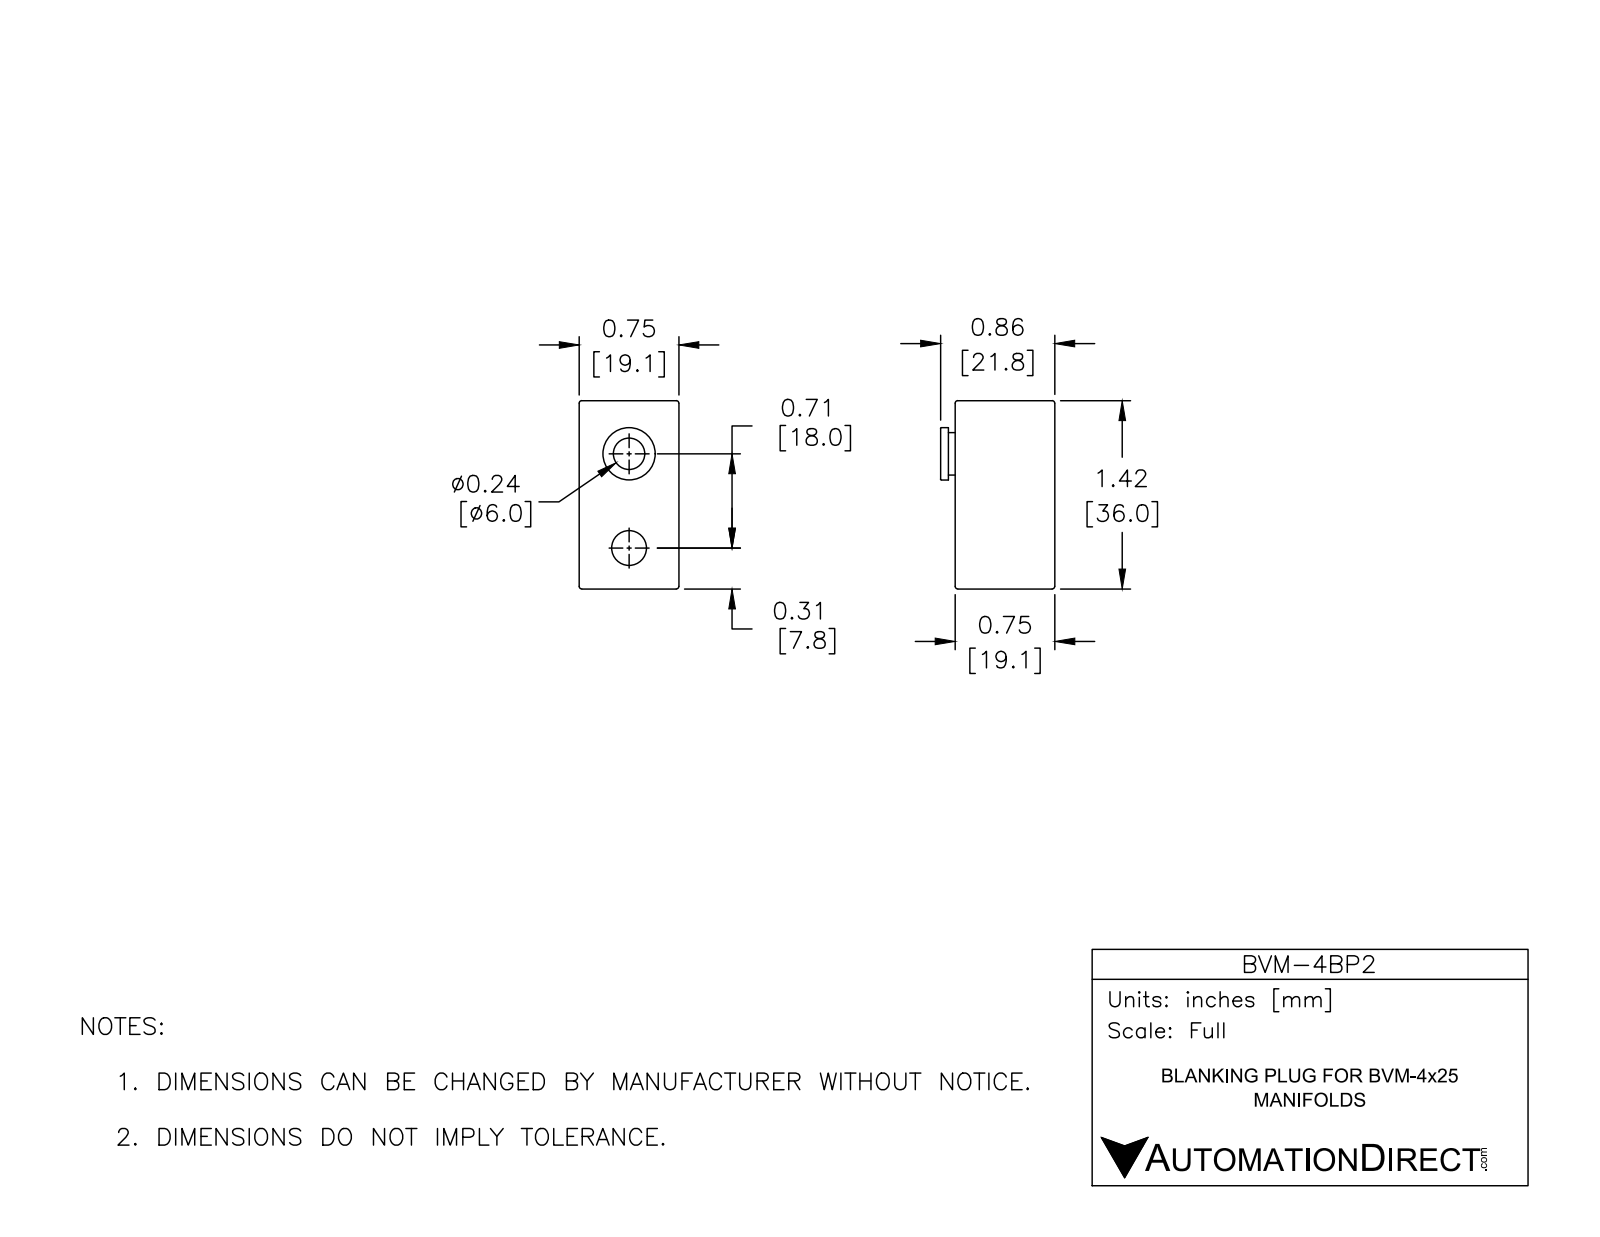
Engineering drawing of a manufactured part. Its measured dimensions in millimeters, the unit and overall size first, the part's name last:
Units: millimetres
Overall size (bounding box): 35.99 × 21.84 × 19.05
Round holes (diameter × count): ⌀6.25 ×2, ⌀6.4 ×1, ⌀7.92 ×1, ⌀10.82 ×1
Round bosses / shafts (diameter × count): ⌀10 ×1, ⌀8.13 ×1
Partial cylindrical surfaces — rounded edges, fillets, slot ends (radius × count): R0.51 ×12
Main face-to-face distances: 19.05, 35.99, 9.4, 9.65, 12.9, 3.5, 6.15, 20.34, 10.94, 7.44
Hole centre spacings: 18.01, 18.03
Volume: 11 811 mm³ · Surface area: 4 416 mm²
Bodies: 1 solid, 61 faces (11 planar, 28 cylindrical, 22 other)
Part name (STEP PRODUCT): BVM-4BP2
STEP written by: SolidWorks 2016 (AUTOMOTIVE_DESIGN)
